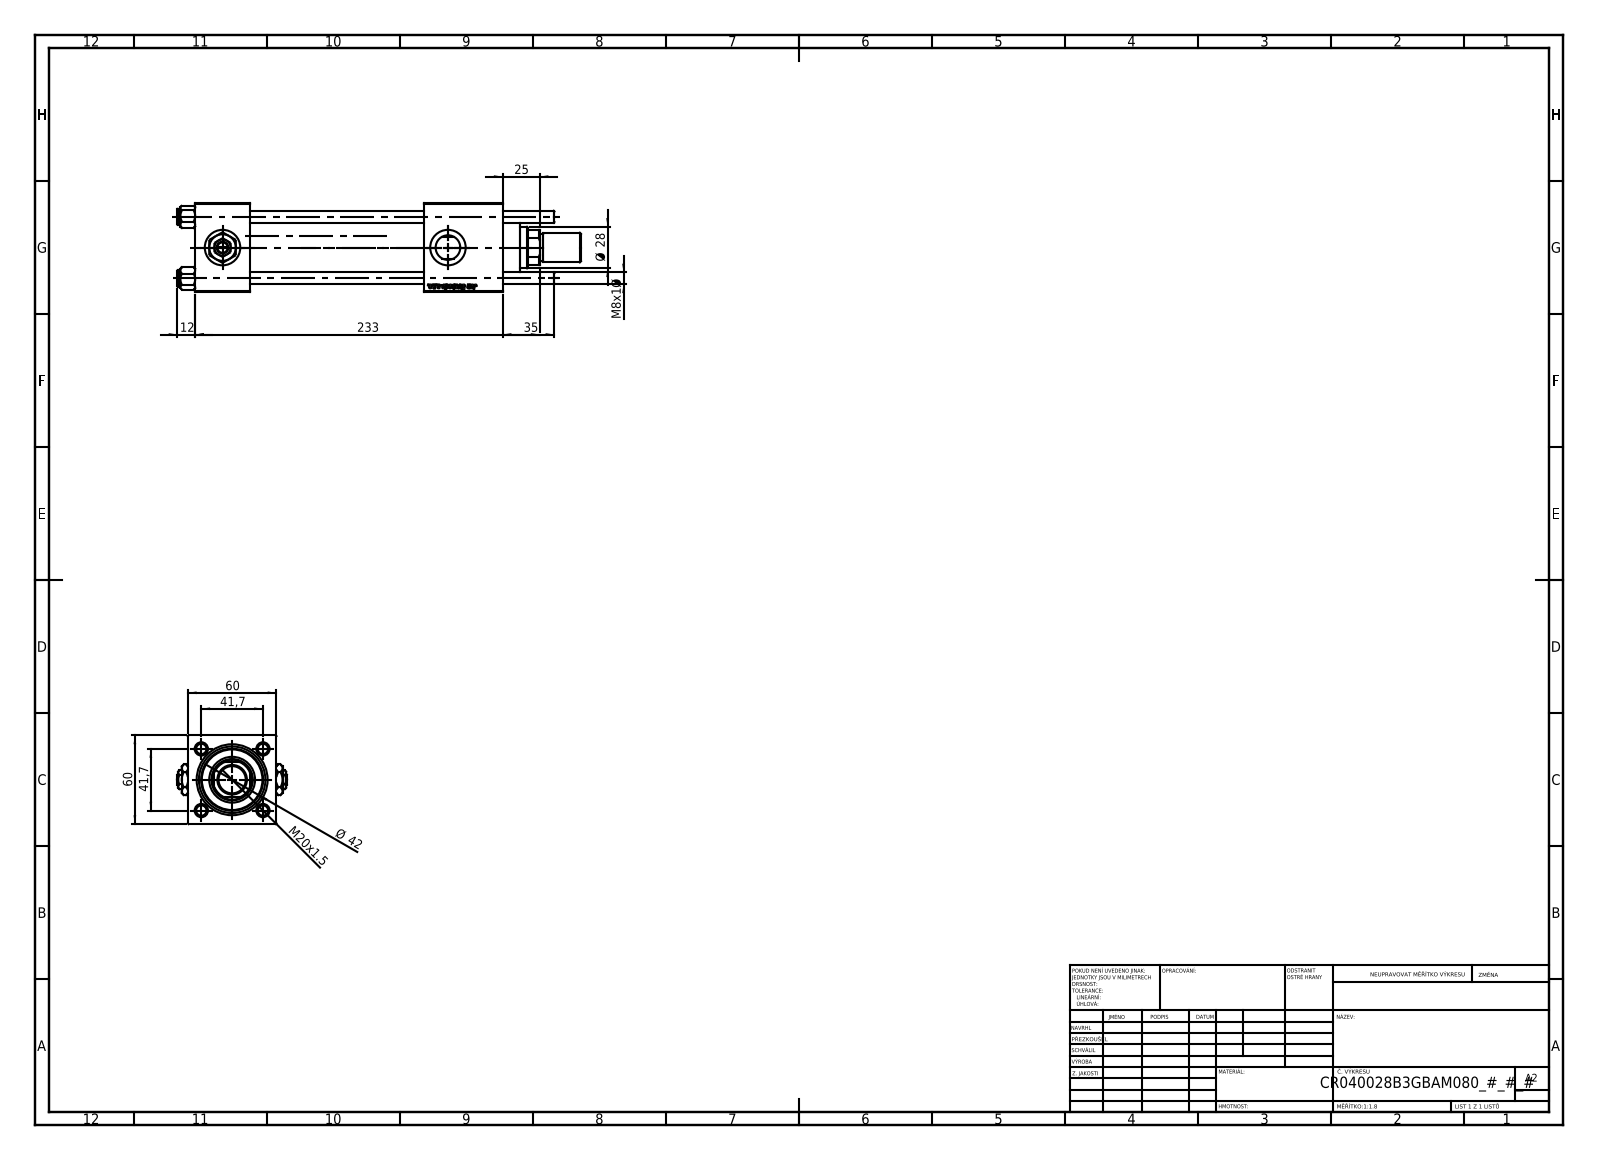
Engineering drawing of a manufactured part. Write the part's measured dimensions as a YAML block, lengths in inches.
part_name: "NUT_M5_B; V215CR_VCP_B; Zatka_pro_OIL_PORT; V215CR_B-1 (+3 more)"
step_written_by: "SolidWorks 2019 (CONFIG_CONTROL_DESIGN)"
units: inches
bodies: {solids: 14, faces: 1273, planar: 485, cylindrical: 92, other: 696}
overall_size: [10.748, 2.913, 2.362]
volume: 31.38
surface_area: 236.7
round_holes:
  - {diameter: 0.315, count: 4}
  - {diameter: 0.276, count: 2}
  - {diameter: 0.656, count: 2}
  - {diameter: 0.945, count: 2}
  - {diameter: 0.728, count: 1}
  - {diameter: 1.102, count: 1}
  - {diameter: 1.22, count: 1}
  - {diameter: 1.575, count: 1}
  - {diameter: 1.772, count: 1}
round_bosses_or_shafts:
  - {diameter: 0.433, count: 4}
  - {diameter: 1.811, count: 1}
  - {diameter: 1.654, count: 1}
  - {diameter: 0.787, count: 1}
  - {diameter: 0.709, count: 1}
partial_cylinders:
  - {radius: 0.531, count: 1}
face_to_face_distances: [2.362, 1.457, 6.102, 4.646, 2.087, 7.059, 5.602, 0.957, 8.189, 6.732]
hole_center_spacings: [1.161, 1.642, 2.322, 6.004]
